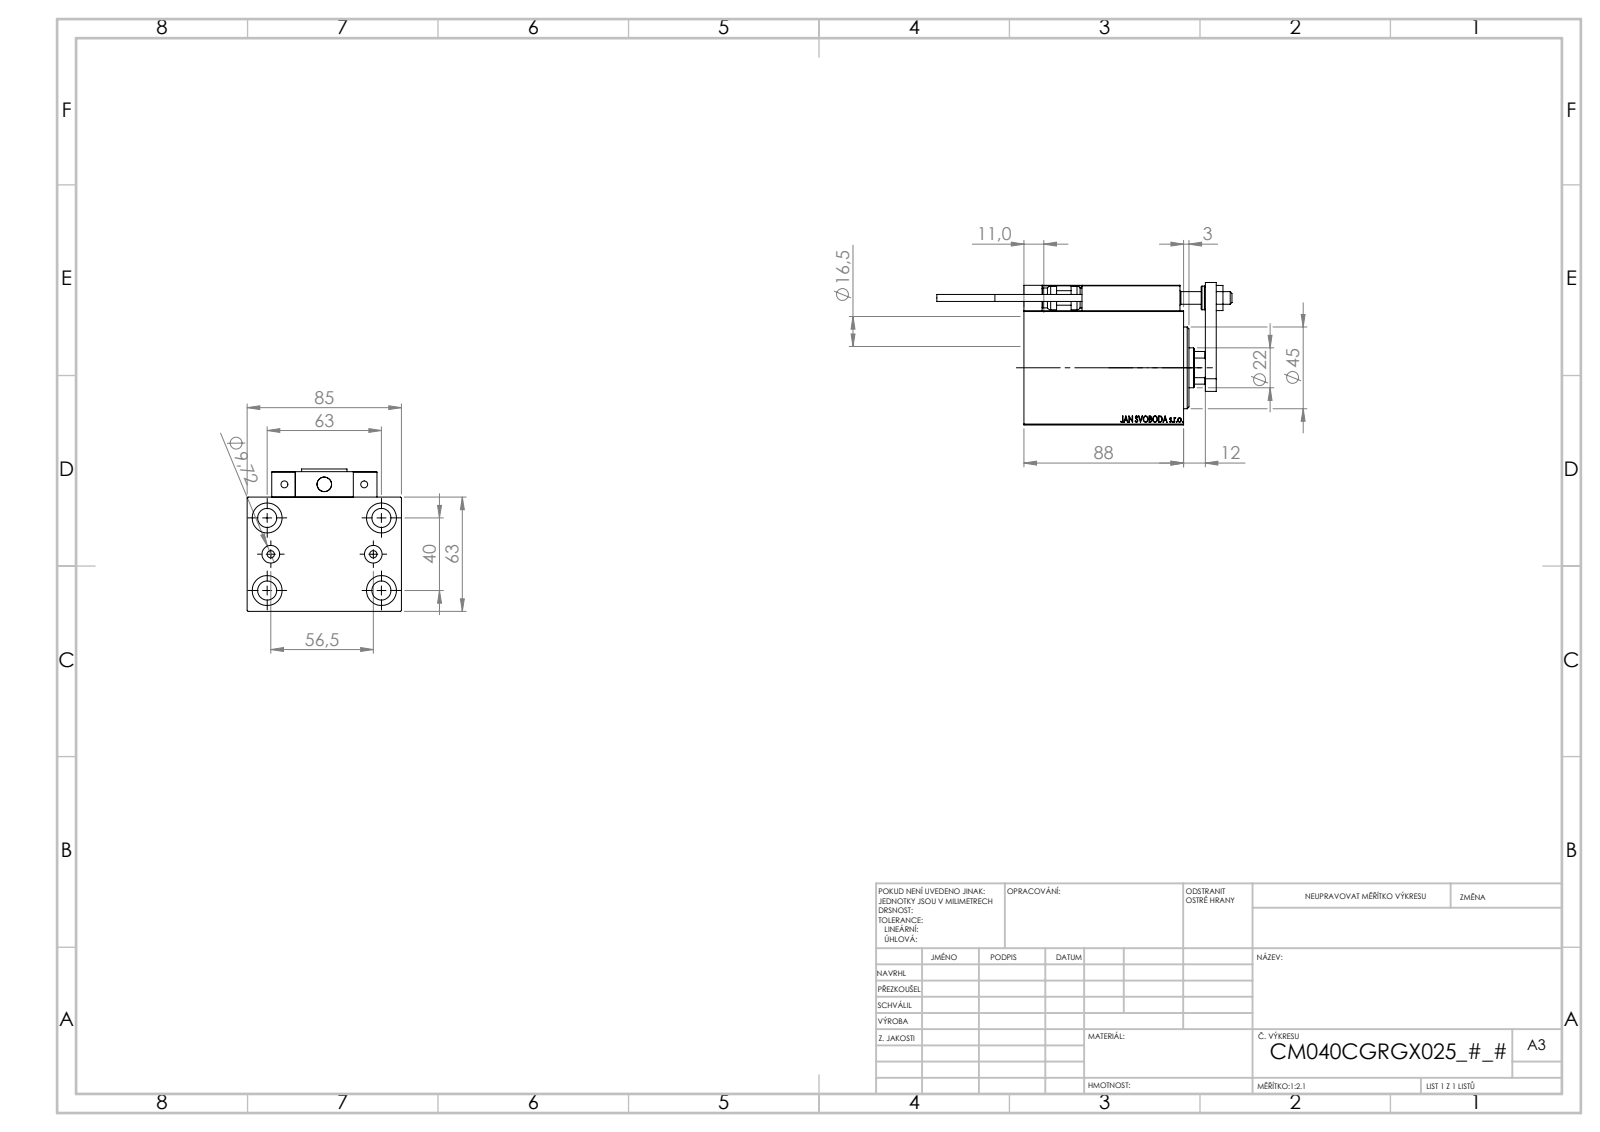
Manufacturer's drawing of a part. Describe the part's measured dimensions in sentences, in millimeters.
The part is named "SWITCH_X_FRONT_BACK; ZARAZKA; SWITCH DIM B,W; ALLEN BOLT D5 (+7 more)". Its 3-D file was written by "SolidWorks 2019 (CONFIG_CONTROL_DESIGN)". It is 23 solids with 1278 faces: 560 planar, 184 cylindrical and 534 other. Overall it measures 162.7 by 85 by 78.5 millimeters. Its volume is 457 865 cubic millimeters and its surface area 105 528 square millimeters. Round holes: 6 of diameter 4, 5 of diameter 8, 5 of diameter 16.5, 4 of diameter 3.2, 4 of diameter 10.5, 2 of diameter 5, 2 of diameter 9.72, 1 of diameter 7, 1 of diameter 12.5, 1 of diameter 22, 1 of diameter 25.5, 1 of diameter 40. Round bosses or shafts: 2 of diameter 5, 2 of diameter 3.8, 1 of diameter 13, 1 of diameter 11. Partial cylindrical surfaces (rounded edges, fillets, slot ends): 30 of radius 0.3, 2 of radius 3, 1 of radius 10.5. The main face-to-face distances are 63, 85, 12, 88, 76, 14, 77, 25, 18, 6. The hole center spacings are 20.26, 37.31, 63.01, 11.37, 20, 28.25, 29.59, 29.69.
